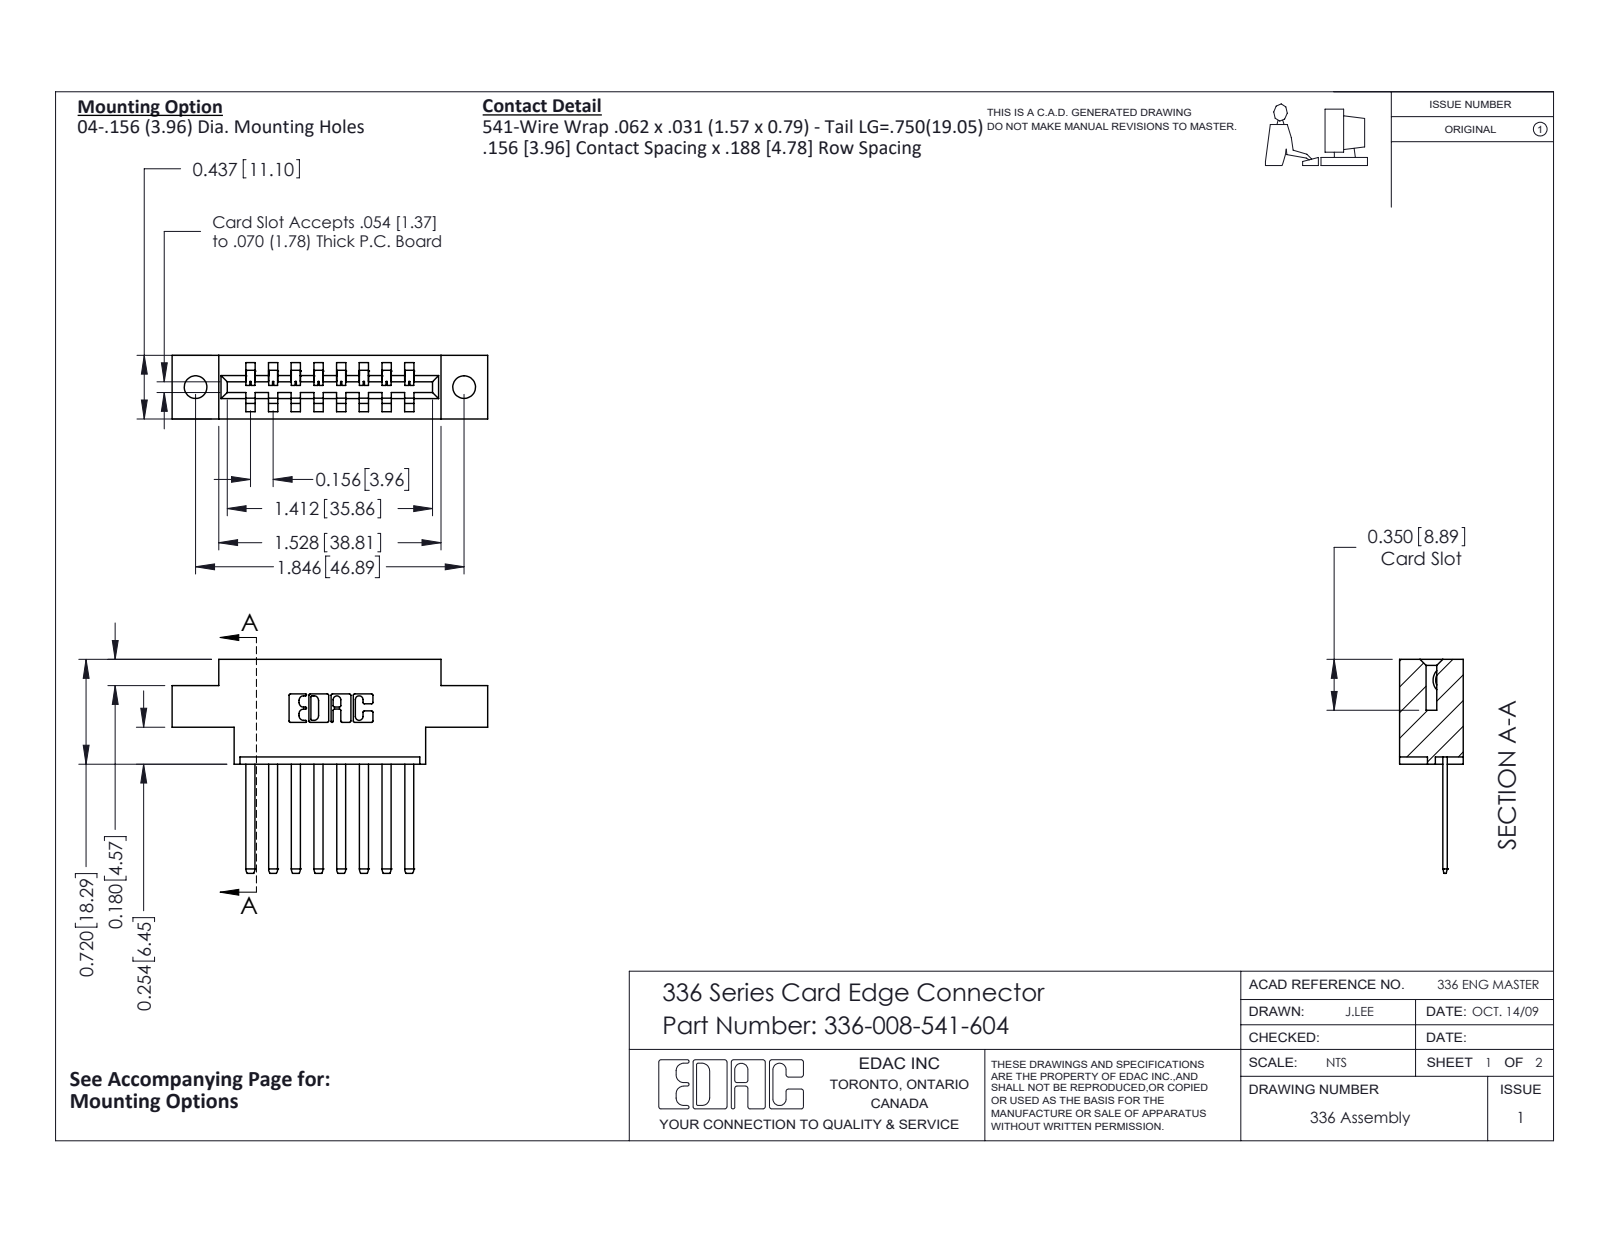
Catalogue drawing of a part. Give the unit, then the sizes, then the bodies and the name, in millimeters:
Units: millimetres
Overall size (bounding box): 55.1 × 37.3 × 11.1
Round holes (diameter × count): ⌀4 ×2
Partial cylindrical surfaces — rounded edges, fillets, slot ends (radius × count): R0.3 ×22, R0.1 ×16, R1.4 ×16, R0.2 ×6, R0.8 ×6, R0.7 ×3, R0.6 ×2, R1 ×2
Main face-to-face distances: 4, 11.1, 11.9, 15.8, 7.9, 7.9, 5.6, 4.6, 9.6, 19.8
Hole centre spacings: 46.9
Volume: 6 950 mm³ · Surface area: 7 019 mm²
Bodies: 9 solids, 518 faces (346 planar, 172 cylindrical, 0 other)
Part name (STEP PRODUCT): 336-290-001_336-290-541; 336 Part_Offset - .156 Dia - TH; 336-008-541-604
STEP written by: SolidWorks 2020 (CONFIG_CONTROL_DESIGN)
